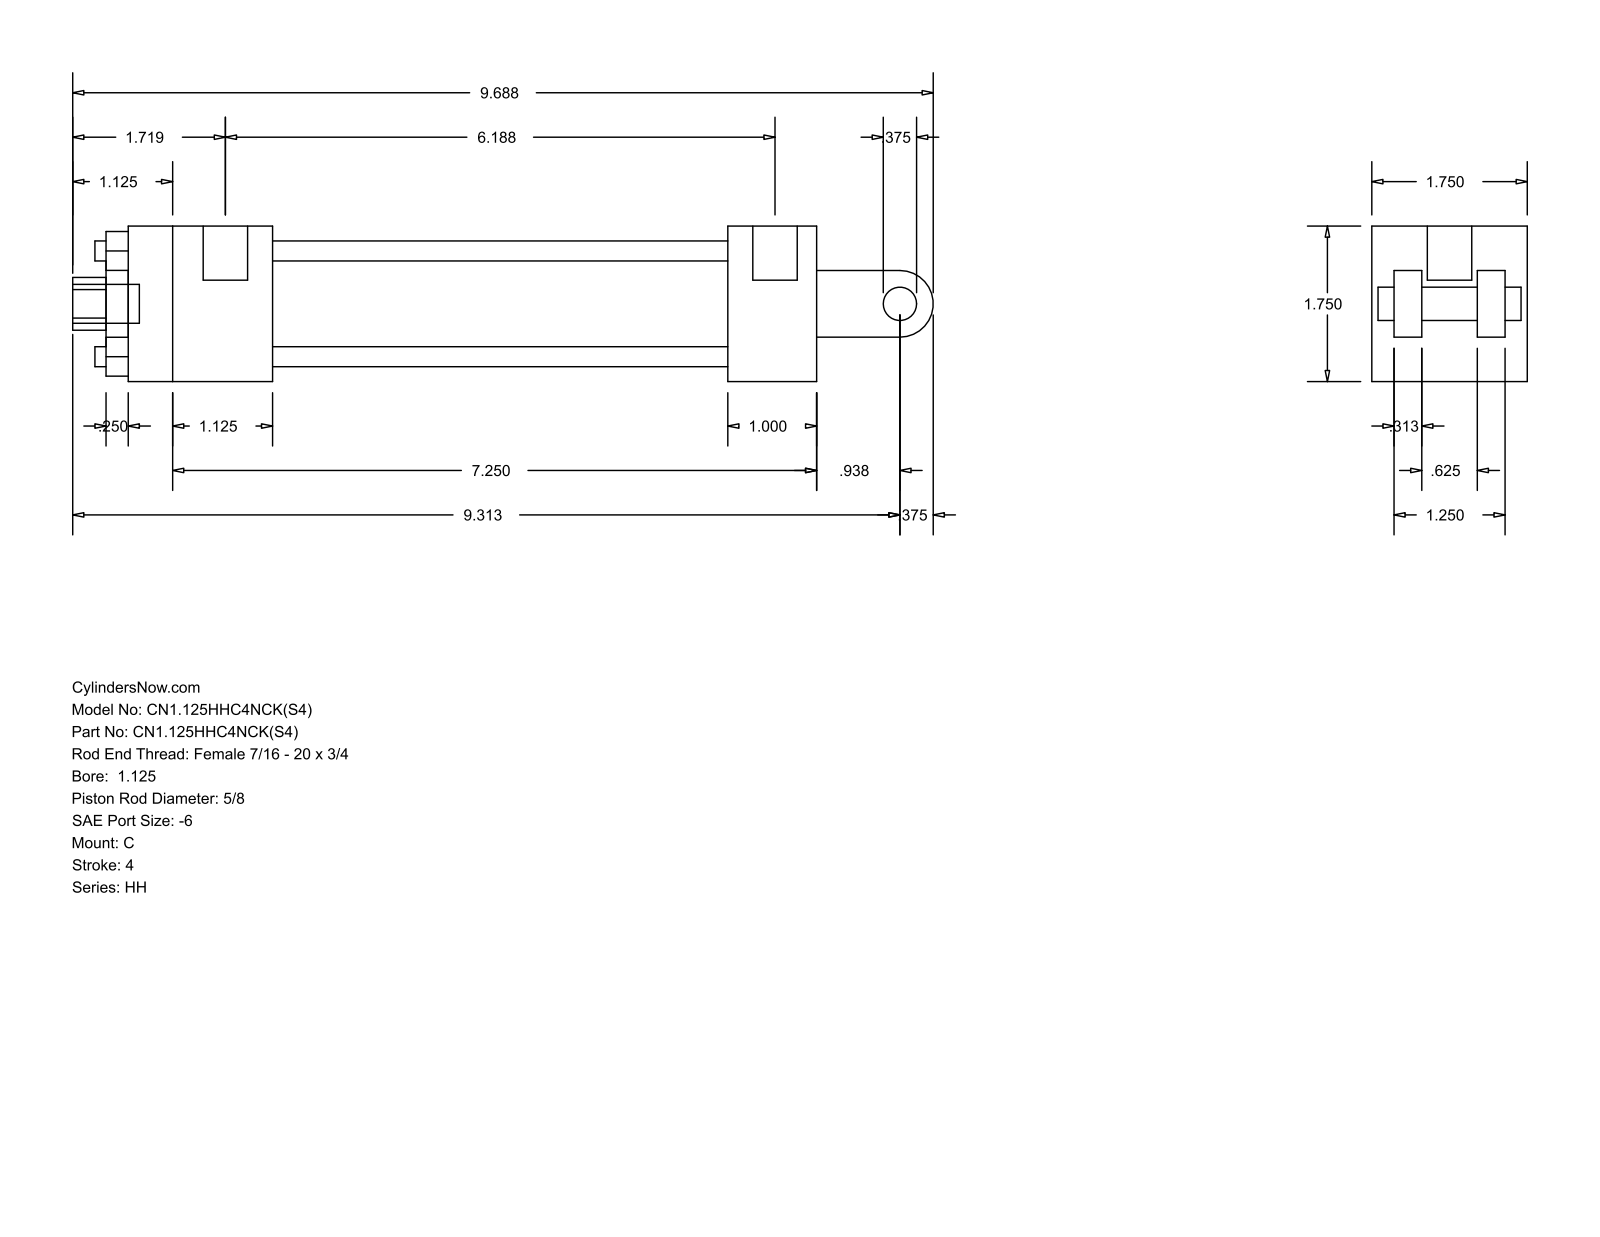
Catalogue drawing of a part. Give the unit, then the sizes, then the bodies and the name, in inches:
Units: inches
Overall size (bounding box): 9.687 × 1.75 × 1.75
Round holes (diameter × count): ⌀0.225 ×4, ⌀0.219 ×2, ⌀0.5 ×1, ⌀0.625 ×1, ⌀1.125 ×1, ⌀1.375 ×1
Round bosses / shafts (diameter × count): ⌀0.219 ×2, ⌀0.5 ×1, ⌀0.437 ×1, ⌀0.375 ×1
Partial cylindrical surfaces — rounded edges, fillets, slot ends (radius × count): R0.297 ×1, R0.375 ×1
Main face-to-face distances: 1.75, 0.25, 1.25, 0.563, 0.5, 1.188, 1.5, 0.313, 0.938, 1
Hole centre spacings: 0.841, 1.19, 1.683
Bodies: 0 solids, 99 faces (70 planar, 29 cylindrical, 0 other)
Part name (STEP PRODUCT): HH_C__0112_0.625
STEP written by: GSSL Pune (CONFIG_CONTROL_DESIGN)
